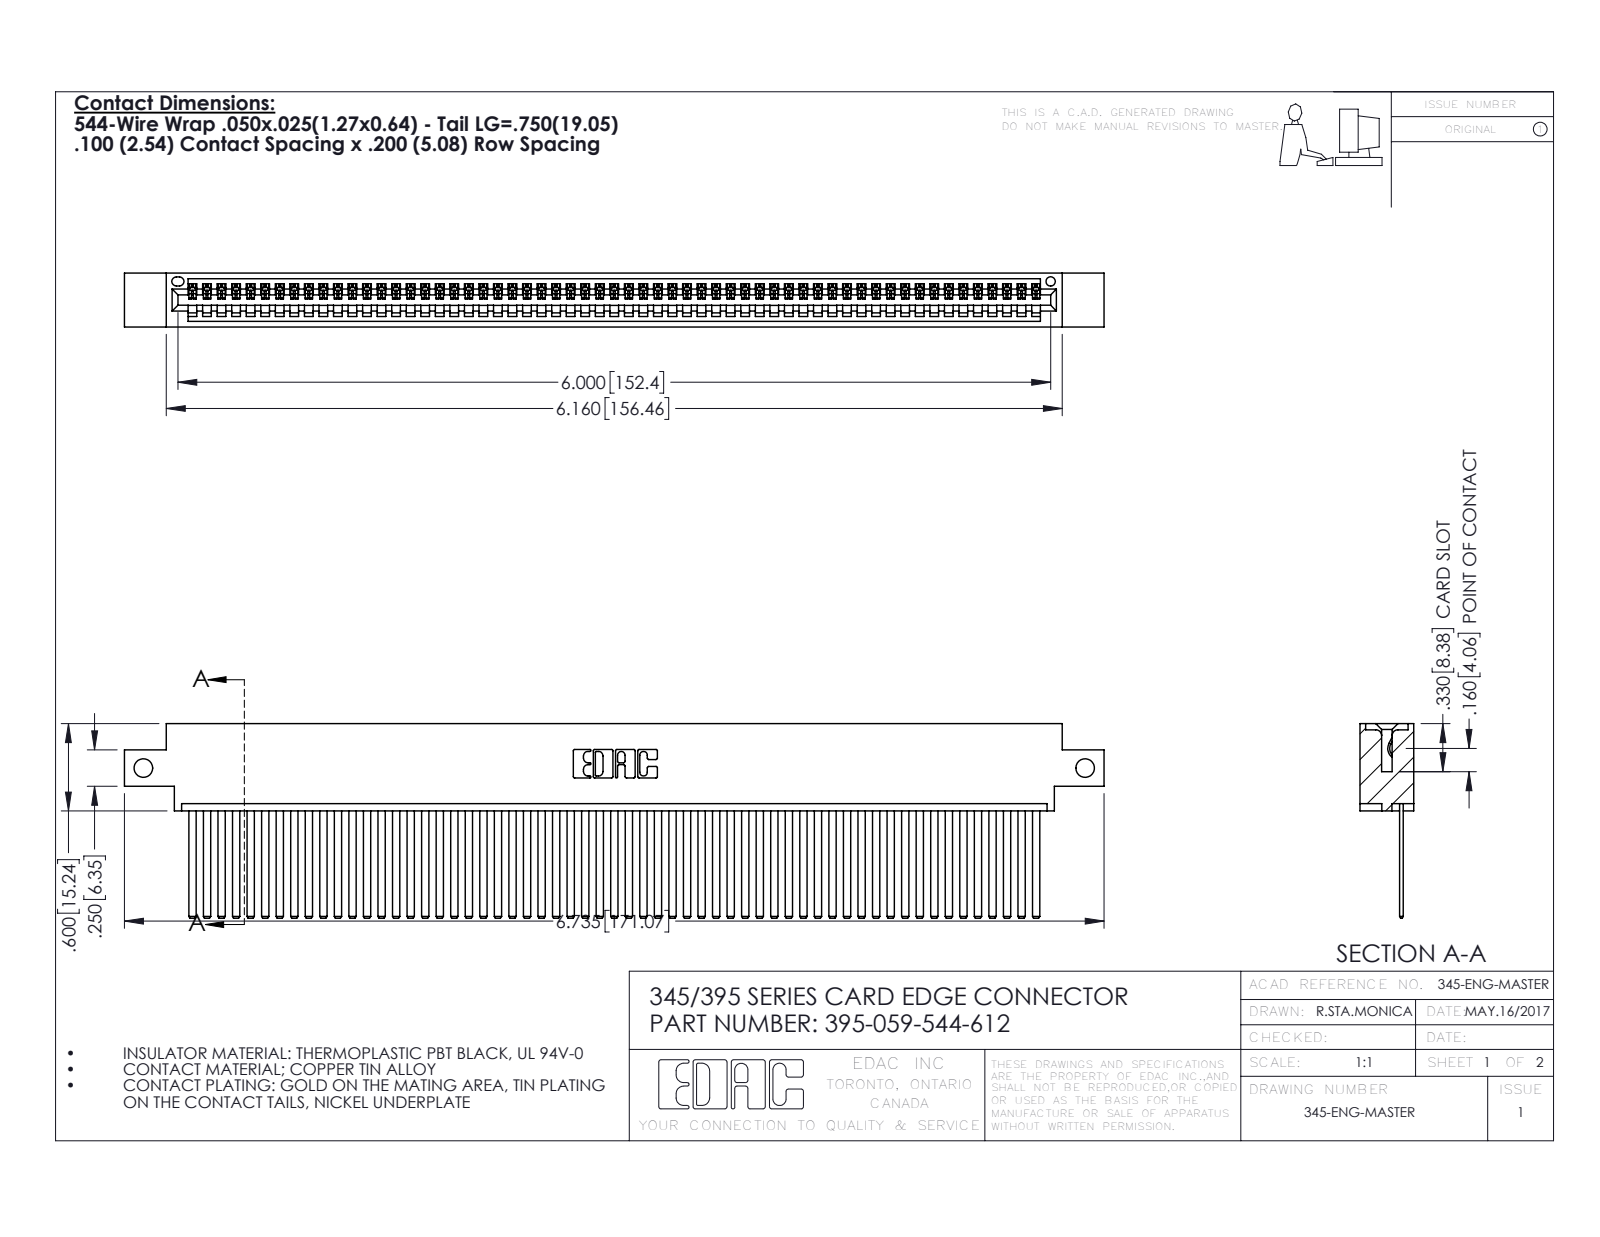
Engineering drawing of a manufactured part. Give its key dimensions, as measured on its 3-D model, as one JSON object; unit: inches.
{"part_name": "395-059-544-612; 345 Part_0.170 Offset - Side Mount; 345-292-001_345-293-144", "step_written_by": "SolidWorks 2016 (CONFIG_CONTROL_DESIGN)", "units": "inches", "bodies": {"solids": 60, "faces": 3198, "planar": 2208, "cylindrical": 990, "other": 0}, "overall_size": [6.735, 1.337, 0.37], "volume_in3": 1.029, "surface_area_in2": 38.26, "round_holes": [[0.128, 2], [0.064, 1]], "partial_cylinders_radius": [[0.006, 118], [0.01, 22], [0.007, 6], [0.031, 6], [0.026, 3], [0.031, 2], [0.04, 2], [0.014, 1]], "face_to_face_distances": [0.072, 0.298, 0.025, 0.098, 0.272, 0.37, 0.2, 0.225, 0.175, 0.149], "hole_center_spacings": [6.475]}
